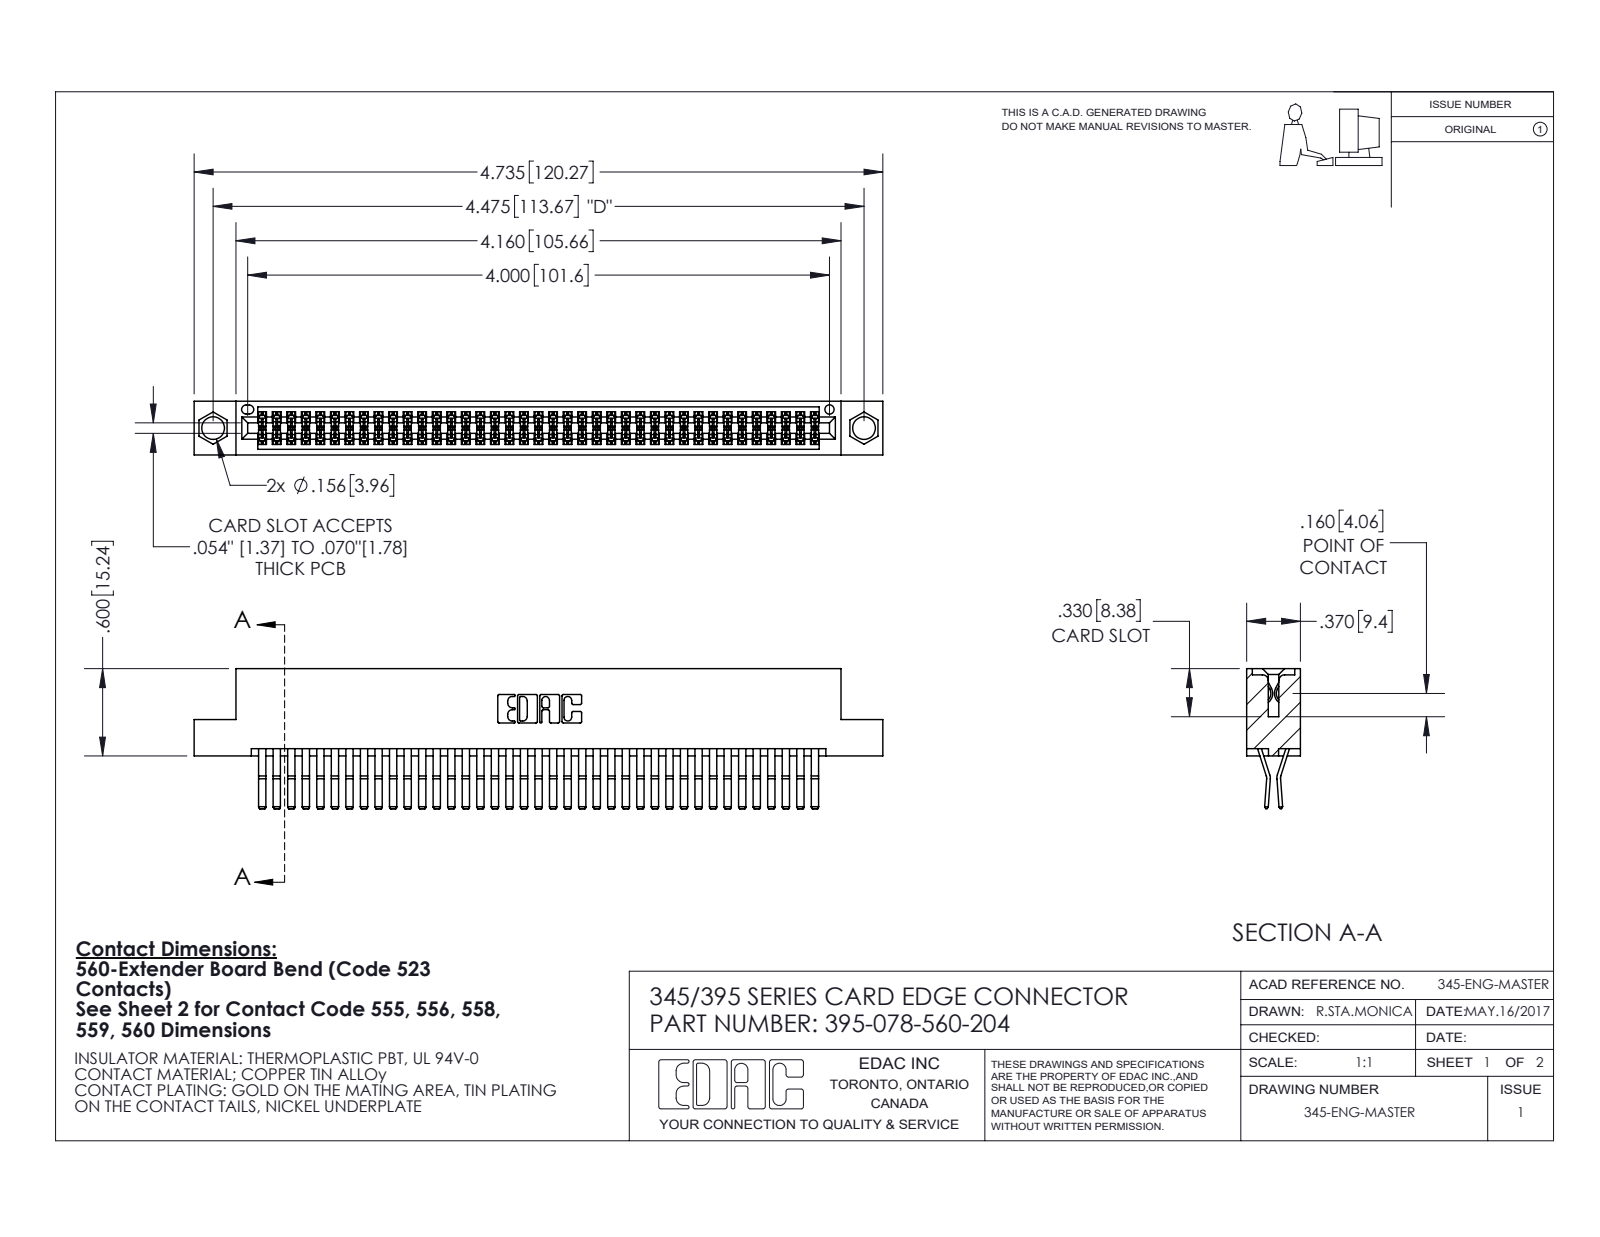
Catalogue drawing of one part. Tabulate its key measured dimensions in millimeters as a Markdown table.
| quantity | value |
| --- | --- |
| part name | 345-292-001_560 Tail; 345 Part_Flush Mounting Lugs - 0.156 Dia-TI; 395-078-560-204 |
| STEP written by | SolidWorks 2020 (CONFIG_CONTROL_DESIGN) |
| units | millimeters |
| bodies | 79 solids, 4196 faces (2668 planar, 1528 cylindrical, 0 other) |
| overall size | 120.3 × 24.4 × 9.4 |
| volume | 12 100 mm³ |
| surface area | 18 940 mm² |
| round holes (diameter × count) | 4 × 2, 1.6 × 1 |
| partial cylindrical surfaces (radius × count) | 0.2 × 117, 0.3 × 22, 0.2 × 6, 0.8 × 6, 0.7 × 3, 0.3 × 2, 0.4 × 2, 0.5 × 2 |
| main face-to-face distances | 0.6, 7.6, 1.8, 9.4, 5.1, 2.5, 6.9, 5.7, 4.4, 3.8 |
| hole center spacings | 6.9, 107.7, 113.7 |
